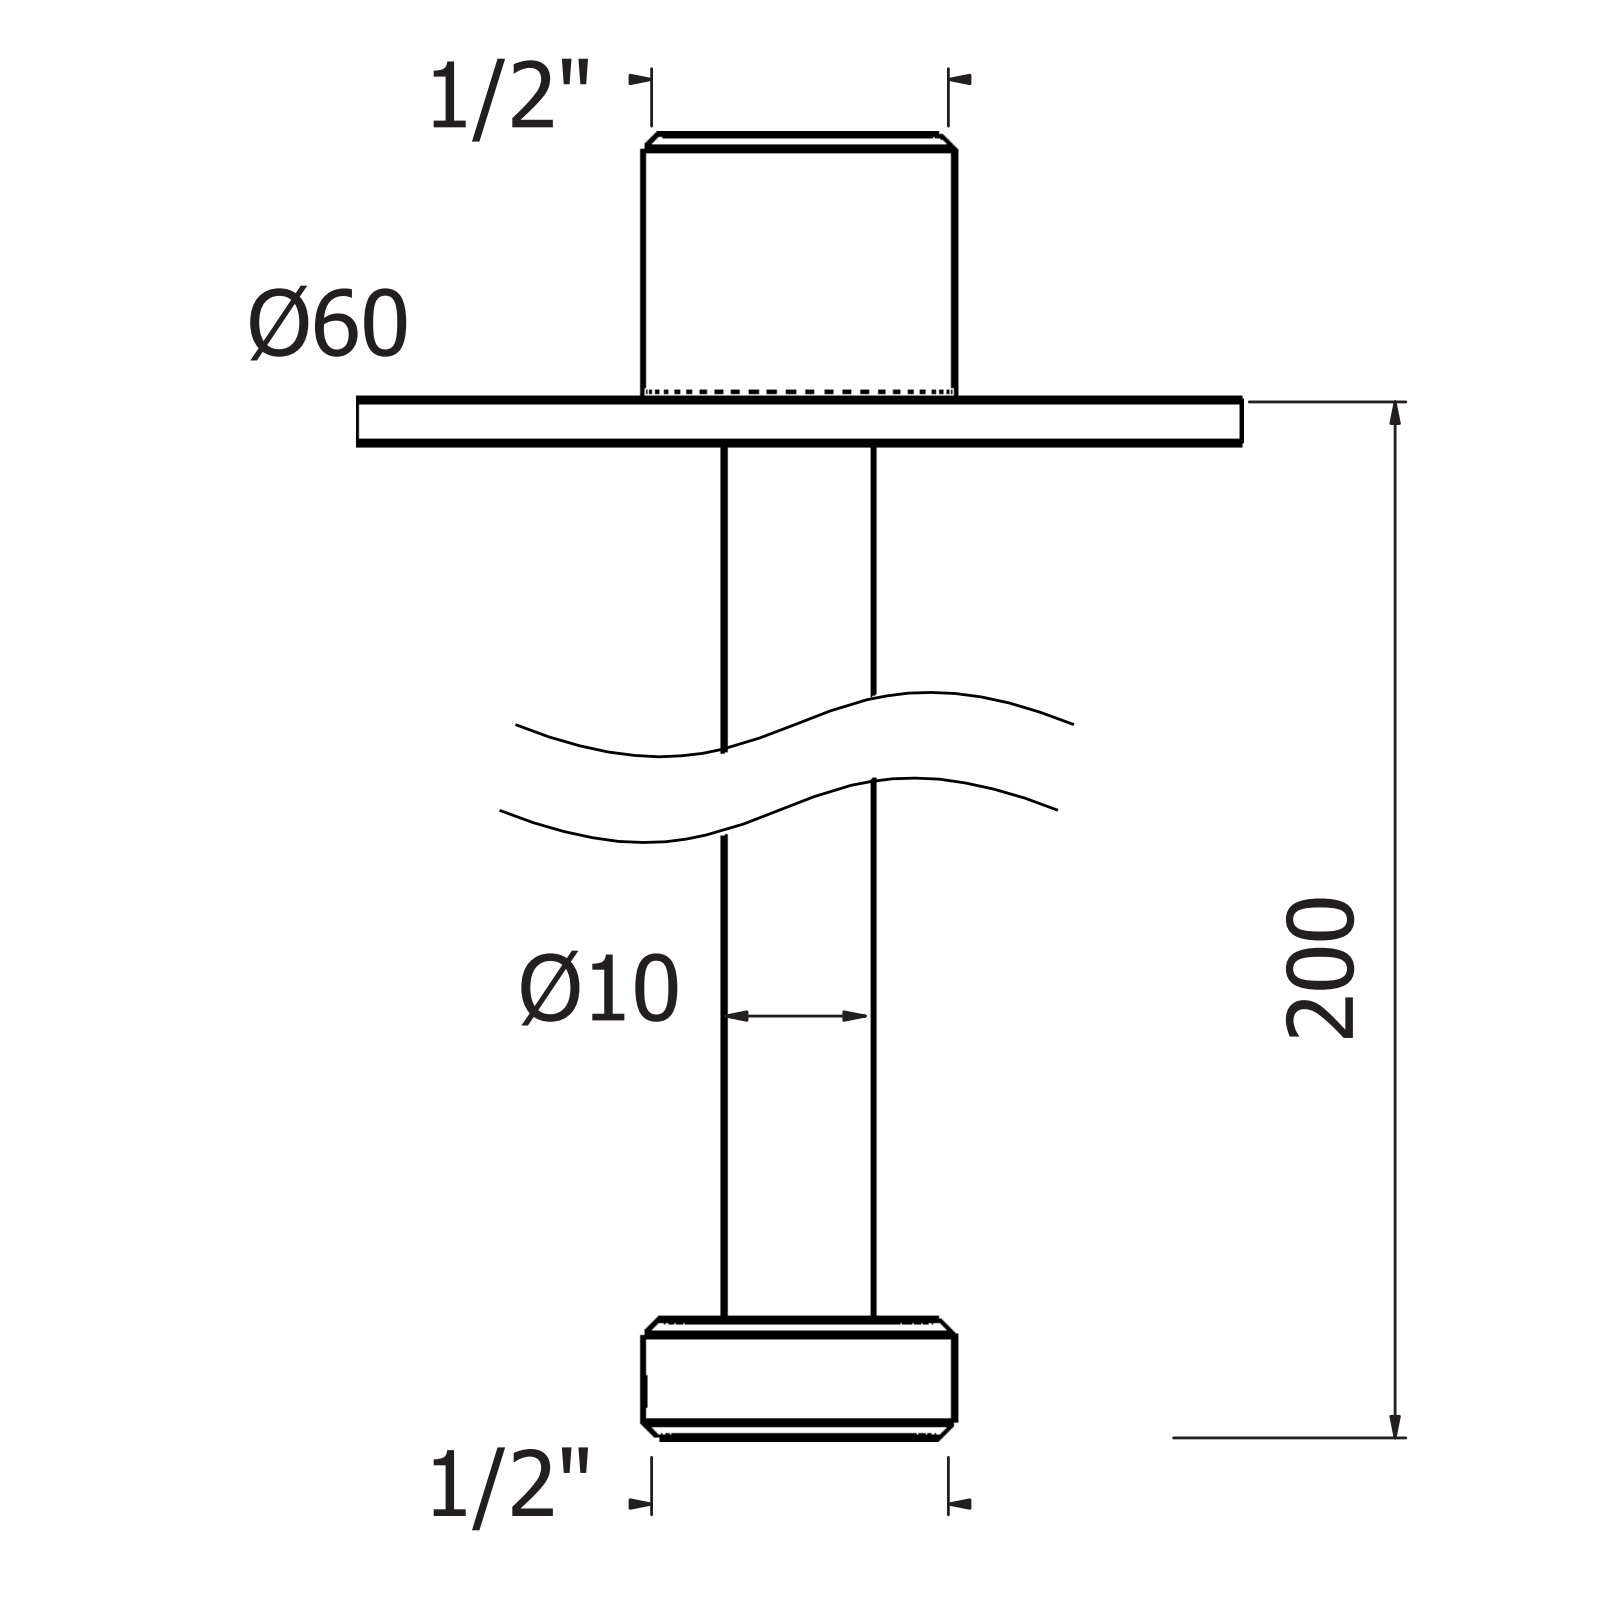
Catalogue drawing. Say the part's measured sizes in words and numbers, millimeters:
The part is named "A.R._24542/20220905; Art.25020". Its 3-D file was written by "Spatial InterOp 3D (AUTOMOTIVE_DESIGN)". It is 4 solids with 41 faces: 18 planar, 16 cylindrical and 7 other. Overall it measures 216.2 by 60 by 60 millimeters. Its volume is 41 224 cubic millimeters and its surface area 37 879 square millimeters. Round holes: 1 of diameter 7, 1 of diameter 10.4, 1 of diameter 14, 1 of diameter 16.4. Round bosses or shafts: 1 of diameter 60, 1 of diameter 20.95, 1 of diameter 10. The main face-to-face distances are 3, 195.2, 198.2, 8, 187.2, 190.2, 211, 203, 15.8, 12.8.
